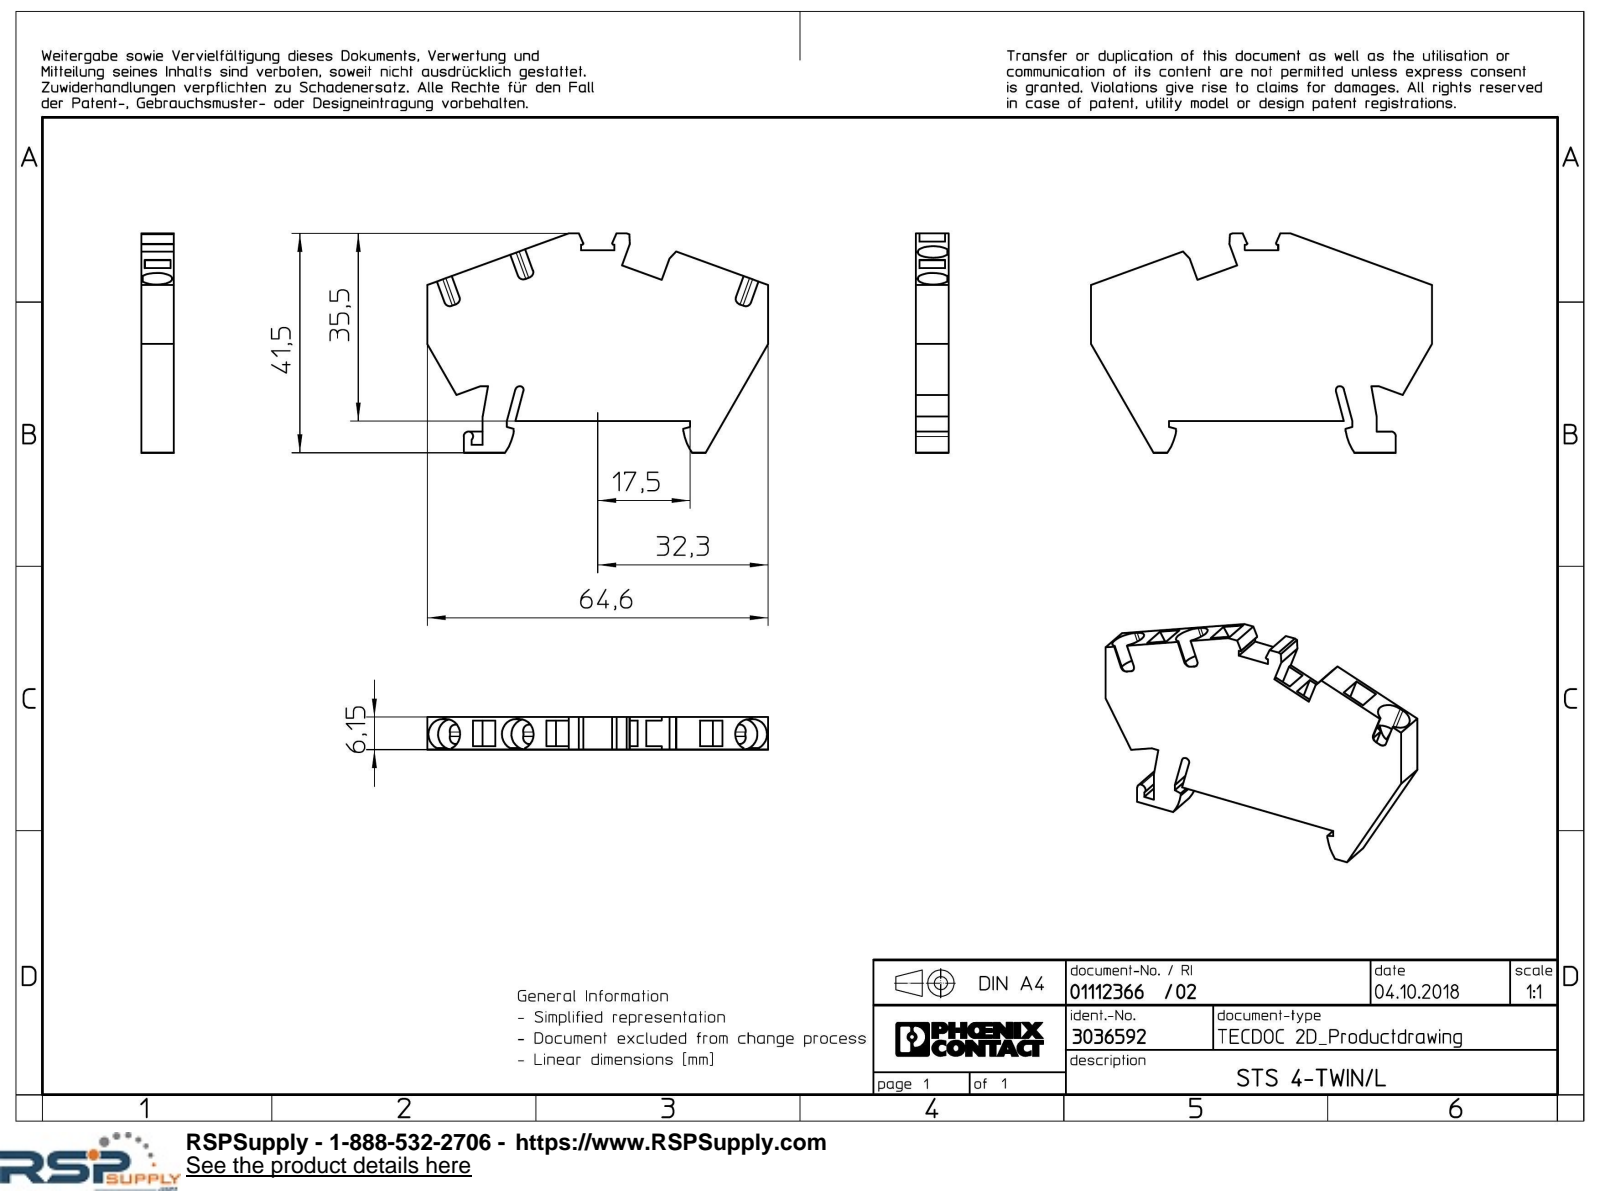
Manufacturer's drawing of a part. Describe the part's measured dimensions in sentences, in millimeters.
The part is named "STS4-TWIN-L-Select". Its 3-D file was written by "Creo Elements/Direct Modeling 18.1I 14-Aug-2016 (C) Parametric Technology GmbH (AUTOMOTIVE_DESIGN)". It is 1 solid with 147 faces: 112 planar, 26 cylindrical and 9 other. Overall it measures 64.6 by 41.5 by 6.15 millimeters. Its volume is 9 938 cubic millimeters and its surface area 6 584 square millimeters. Partial cylindrical surfaces (rounded edges, fillets, slot ends): 6 of radius 1, 6 of radius 1.45, 6 of radius 2.9, 2 of radius 0.17, 2 of radius 9.5, 1 of radius 0.7, 1 of radius 0.8, 1 of radius 0.9. The main face-to-face distances are 6.15, 0.65, 5.5, 4.85, 3.15, 8.45, 8, 14.81, 1.05, 4.75.
